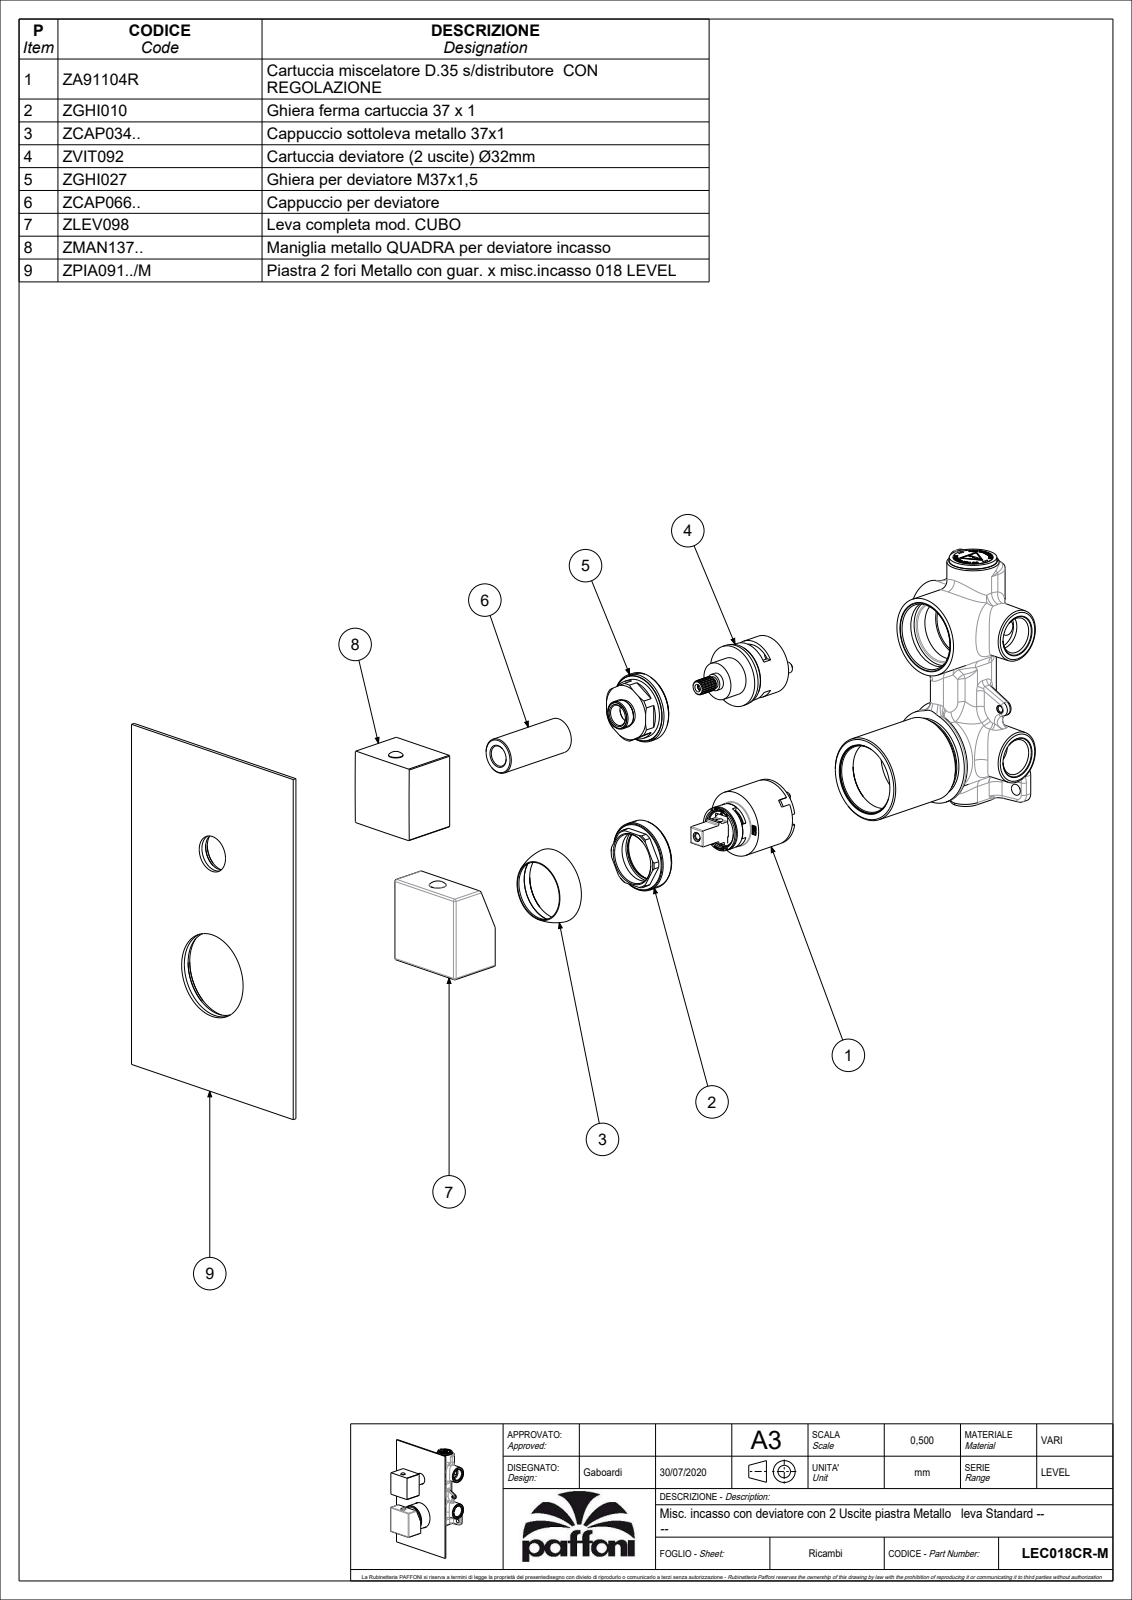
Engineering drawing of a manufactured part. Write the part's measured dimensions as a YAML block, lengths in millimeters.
part_name: "LEC018CR-M"
step_written_by: "CREO PARAMETRIC BY PTC INC, 2020044 (CONFIG_CONTROL_DESIGN)"
units: millimeters
bodies: {solids: 4, faces: 989, planar: 587, cylindrical: 244, other: 158}
overall_size: [190, 120, 56.39]
volume: 128850
surface_area: 97613
round_holes:
  - {diameter: 4, count: 2}
  - {diameter: 11, count: 2}
  - {diameter: 19.5, count: 2}
  - {diameter: 36, count: 2}
  - {diameter: 3, count: 1}
  - {diameter: 3.2, count: 1}
  - {diameter: 3.3, count: 1}
  - {diameter: 4.2, count: 1}
  - {diameter: 4.5, count: 1}
  - {diameter: 5, count: 1}
  - {diameter: 5.5, count: 1}
  - {diameter: 6, count: 1}
round_bosses_or_shafts:
  - {diameter: 5, count: 2}
  - {diameter: 44.8, count: 1}
  - {diameter: 35, count: 1}
  - {diameter: 25, count: 1}
  - {diameter: 23.5, count: 1}
  - {diameter: 23.4, count: 1}
  - {diameter: 21.8, count: 1}
  - {diameter: 18.7, count: 1}
partial_cylinders:
  - {radius: 0.15, count: 11}
  - {radius: 1, count: 10}
  - {radius: 0.5, count: 6}
  - {radius: 0.3, count: 4}
  - {radius: 3.95, count: 1}
  - {radius: 7, count: 1}
  - {radius: 9.3, count: 1}
  - {radius: 10.85, count: 1}
face_to_face_distances: [2, 40, 2.5, 42.5, 45, 54.6, 52.6, 3, 110.5, 70.5]
hole_center_spacings: [0.7, 10, 14.1, 14.8, 58, 68]
